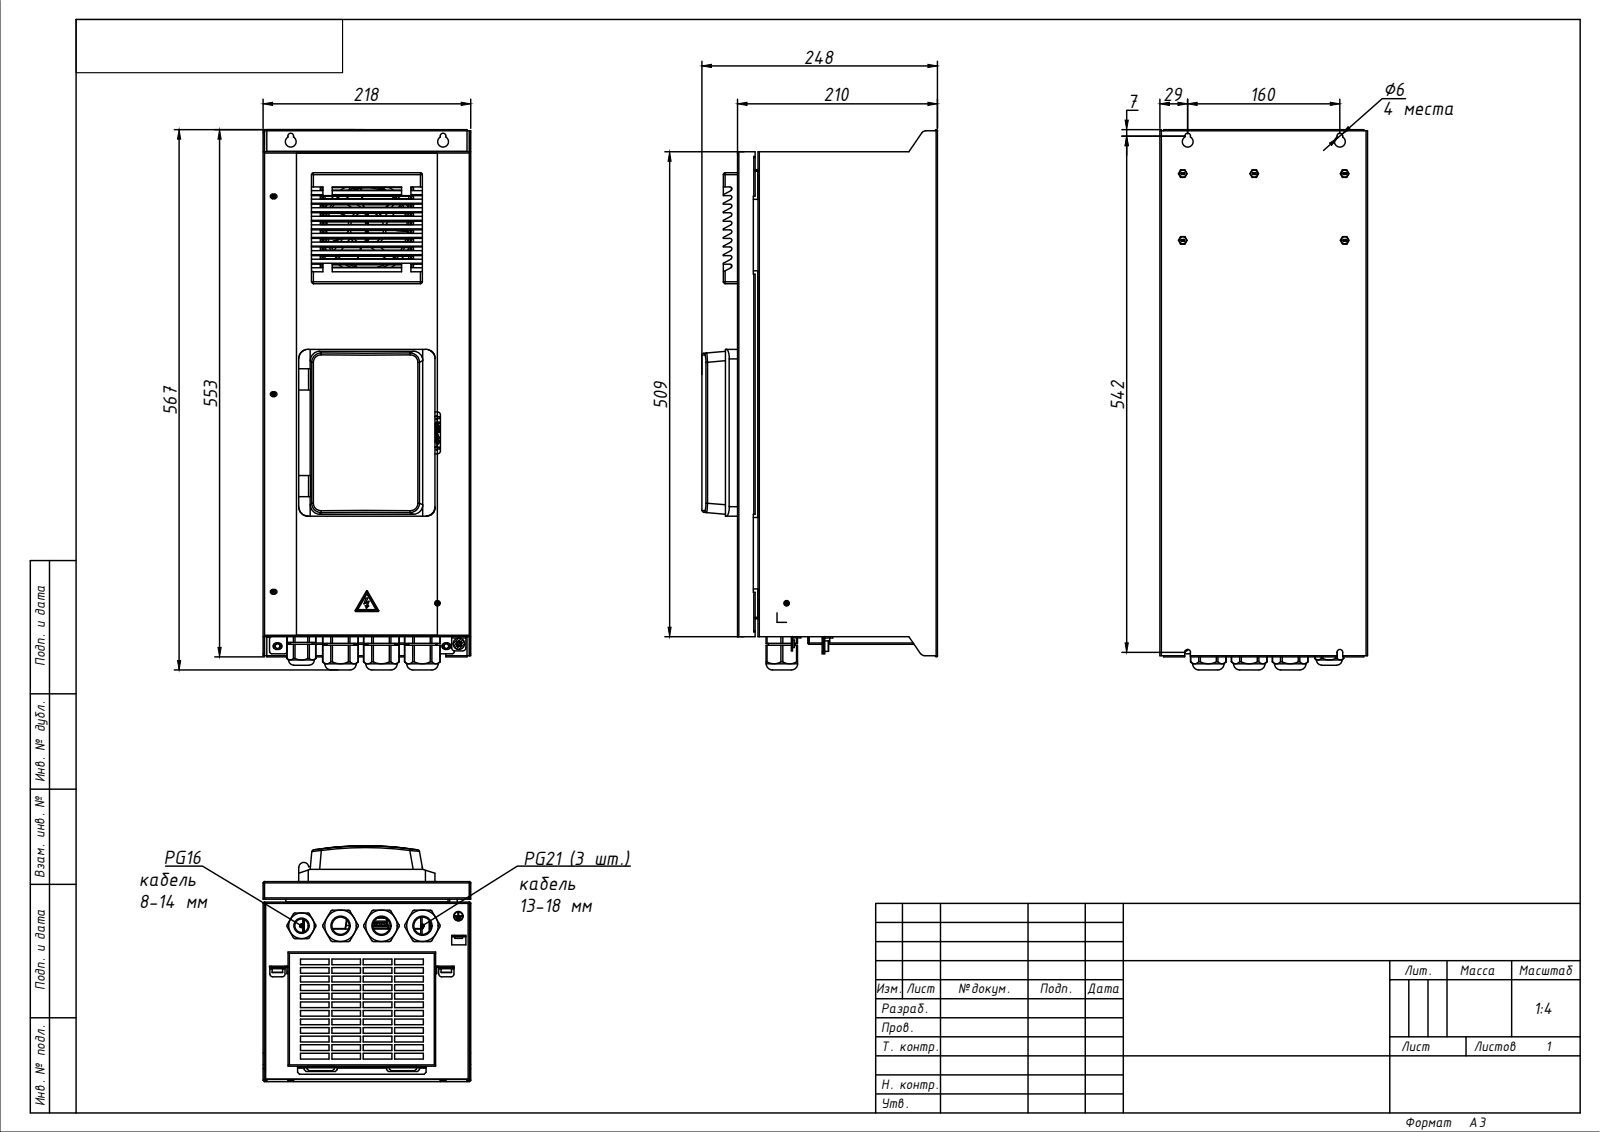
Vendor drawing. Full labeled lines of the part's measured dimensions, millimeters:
Part name (STEP PRODUCT): VF-101-P11K-0025-A-T4-C54-B-H - VF-101-P15K-0032-A-T4-C54-B-H; Корпус 2; Крышка 2; Сальник PG 16 диаметр проводника 9-13мм IP54 IEK (+3 more)
STEP written by: C3D Toolkit (AP242_MANAGED_MODEL_BASED_3D_ENGINEERING_MIM_LF)
Units: millimetres
Bodies: 24 solids, 1576 faces (1102 planar, 184 cylindrical, 290 other)
Overall size (bounding box): 573.4 × 248 × 218
Volume: 24 360 000 mm³ · Surface area: 780 572 mm²
Round holes (diameter × count): ⌀22 ×4, ⌀18.5 ×3, ⌀19 ×3, ⌀22.3 ×3, ⌀26.3 ×3, ⌀27 ×3, ⌀27.5 ×3, ⌀28 ×3, ⌀11.5 ×2, ⌀14 ×1, ⌀14.6 ×1, ⌀15.5 ×1
Round bosses / shafts (diameter × count): ⌀34.5 ×3, ⌀31.3 ×3, ⌀28 ×3, ⌀27 ×3, ⌀26 ×3, ⌀27 ×1, ⌀25 ×1, ⌀20 ×1
Partial cylindrical surfaces — rounded edges, fillets, slot ends (radius × count): R2 ×26, R5 ×12, R3 ×6, R1 ×4, R10 ×4, R17.5 ×3, R17.75 ×3, R19.5 ×3
Main face-to-face distances: 210, 218, 509, 1, 8, 517, 7, 516, 248, 38
Hole centre spacings: 43.5, 40.5, 84, 87, 127.5, 160
